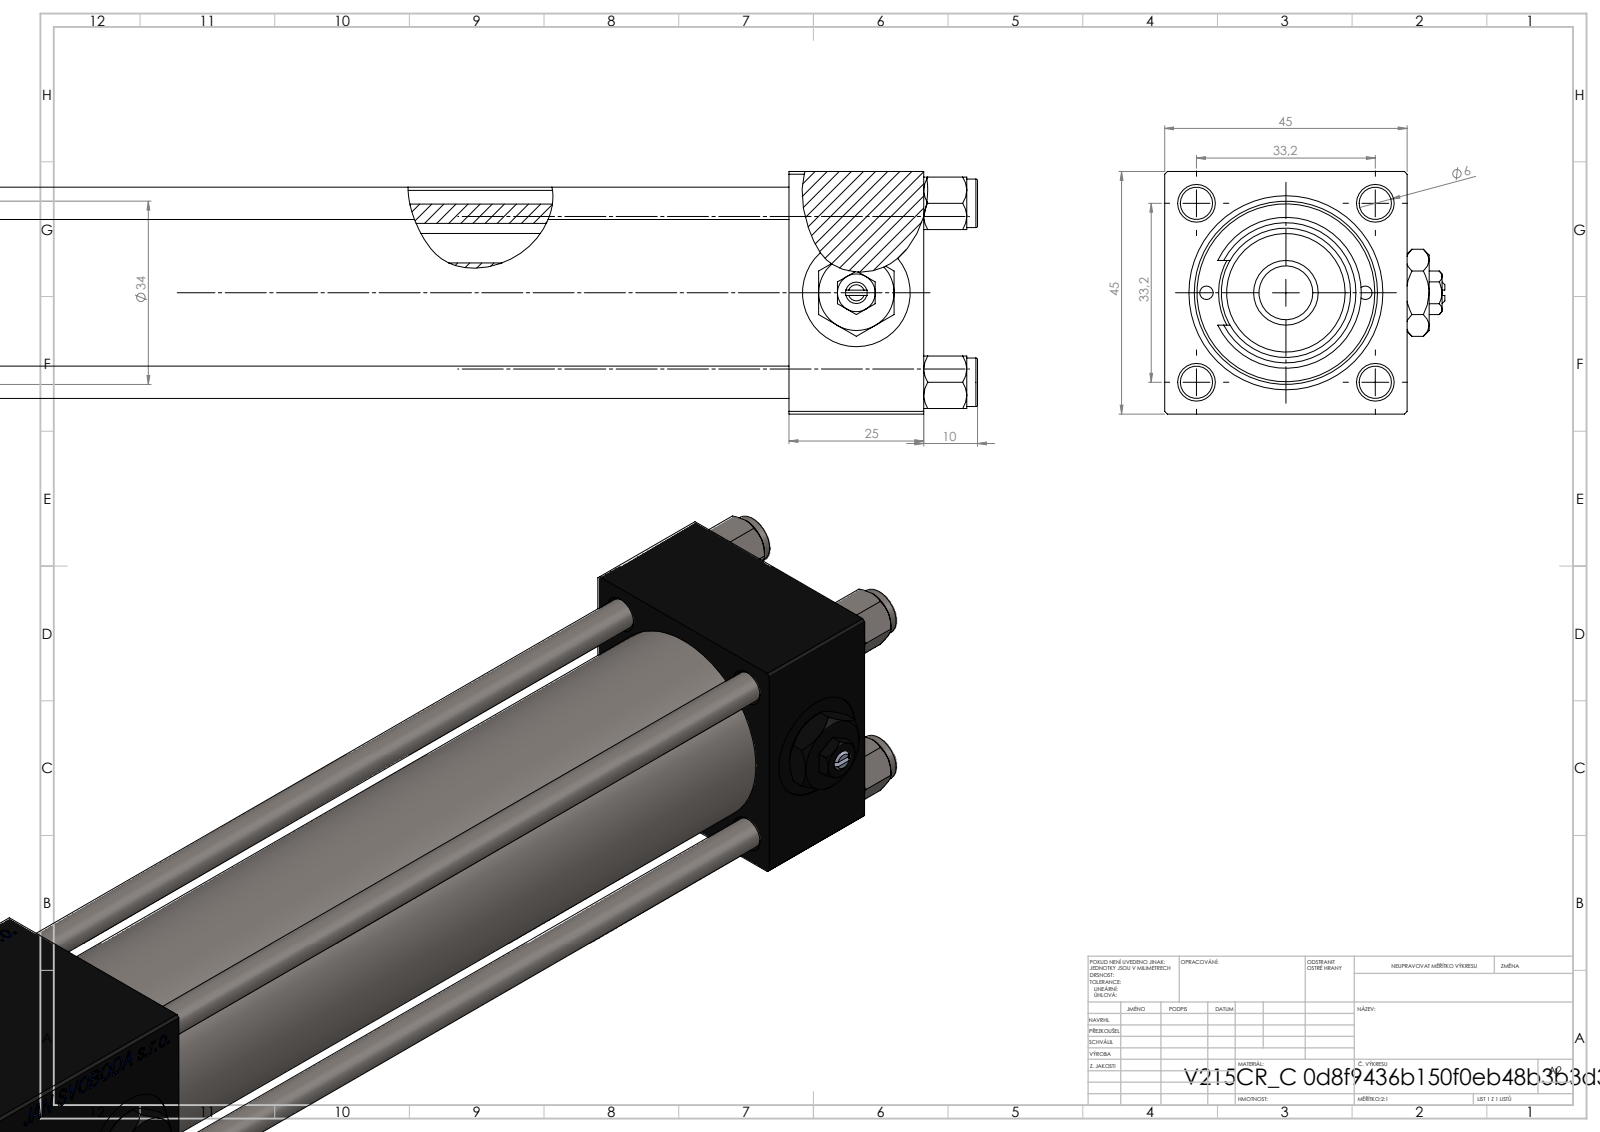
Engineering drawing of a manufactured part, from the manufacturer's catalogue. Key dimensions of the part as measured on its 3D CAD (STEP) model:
Part name (STEP PRODUCT): V215CR_C_TYCINKA; V215CR_C_Body; V215_VC_A; FEMALE_PART_FOR_DFA (+4 more)
STEP written by: SolidWorks 2019 (CONFIG_CONTROL_DESIGN)
Units: millimetres
Bodies: 15 solids, 1339 faces (602 planar, 115 cylindrical, 622 other)
Overall size (bounding box): 324 × 52 × 45
Volume: 312 444 mm³ · Surface area: 118 796 mm²
Round holes (diameter × count): ⌀6 ×4, ⌀2.5 ×2, ⌀7 ×2, ⌀13.16 ×2, ⌀20 ×2, ⌀10.5 ×1, ⌀22 ×1, ⌀24 ×1, ⌀25 ×1, ⌀32 ×1, ⌀33 ×1
Round bosses / shafts (diameter × count): ⌀9 ×4, ⌀38 ×1, ⌀34 ×1, ⌀28 ×1, ⌀18 ×1, ⌀12 ×1, ⌀11 ×1, ⌀10 ×1
Partial cylindrical surfaces — rounded edges, fillets, slot ends (radius × count): R9.75 ×1, R10.5 ×1
Main face-to-face distances: 45, 25, 228, 180, 155, 203, 44.8, 13, 48, 199.3
Hole centre spacings: 16.7, 23.48, 33.2, 35.47, 14.75, 46.95, 29.5, 180.5
